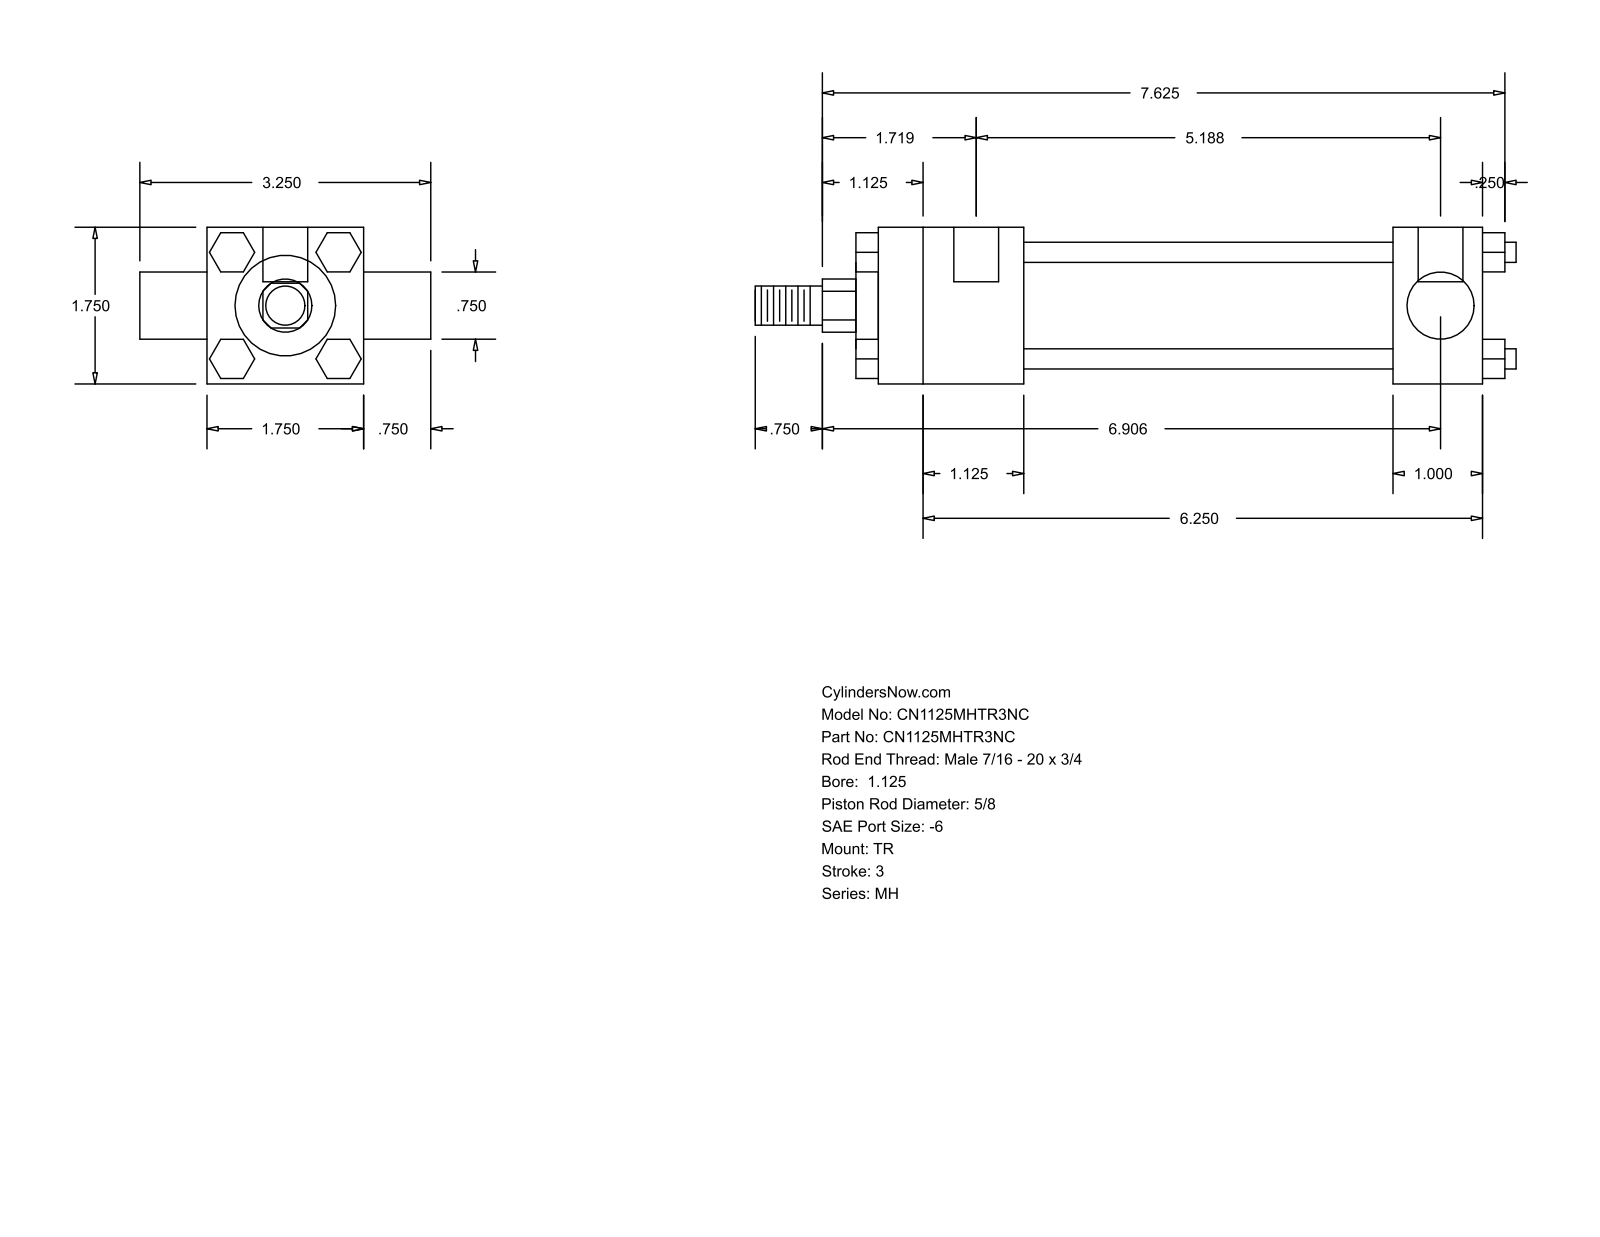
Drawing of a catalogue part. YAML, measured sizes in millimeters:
part_name: "MH_TR__0112_0.625"
step_written_by: "GSSL Pune (CONFIG_CONTROL_DESIGN)"
units: millimeters
bodies: {solids: 0, faces: 120, planar: 92, cylindrical: 28, other: 0}
overall_size: [215.9, 82.55, 44.45]
round_holes:
  - {diameter: 5.56, count: 3}
  - {diameter: 12.7, count: 2}
round_bosses_or_shafts:
  - {diameter: 5.71, count: 4}
  - {diameter: 34.92, count: 1}
  - {diameter: 28.57, count: 1}
  - {diameter: 19.05, count: 1}
  - {diameter: 15.88, count: 1}
  - {diameter: 11.11, count: 1}
partial_cylinders:
  - {radius: 7.54, count: 1}
face_to_face_distances: [44.46, 11.11, 104.78, 130.17, 25.39, 41.27, 146.05, 171.44, 47.62, 6.35]
hole_center_spacings: [3.17, 128.59, 131.76]
